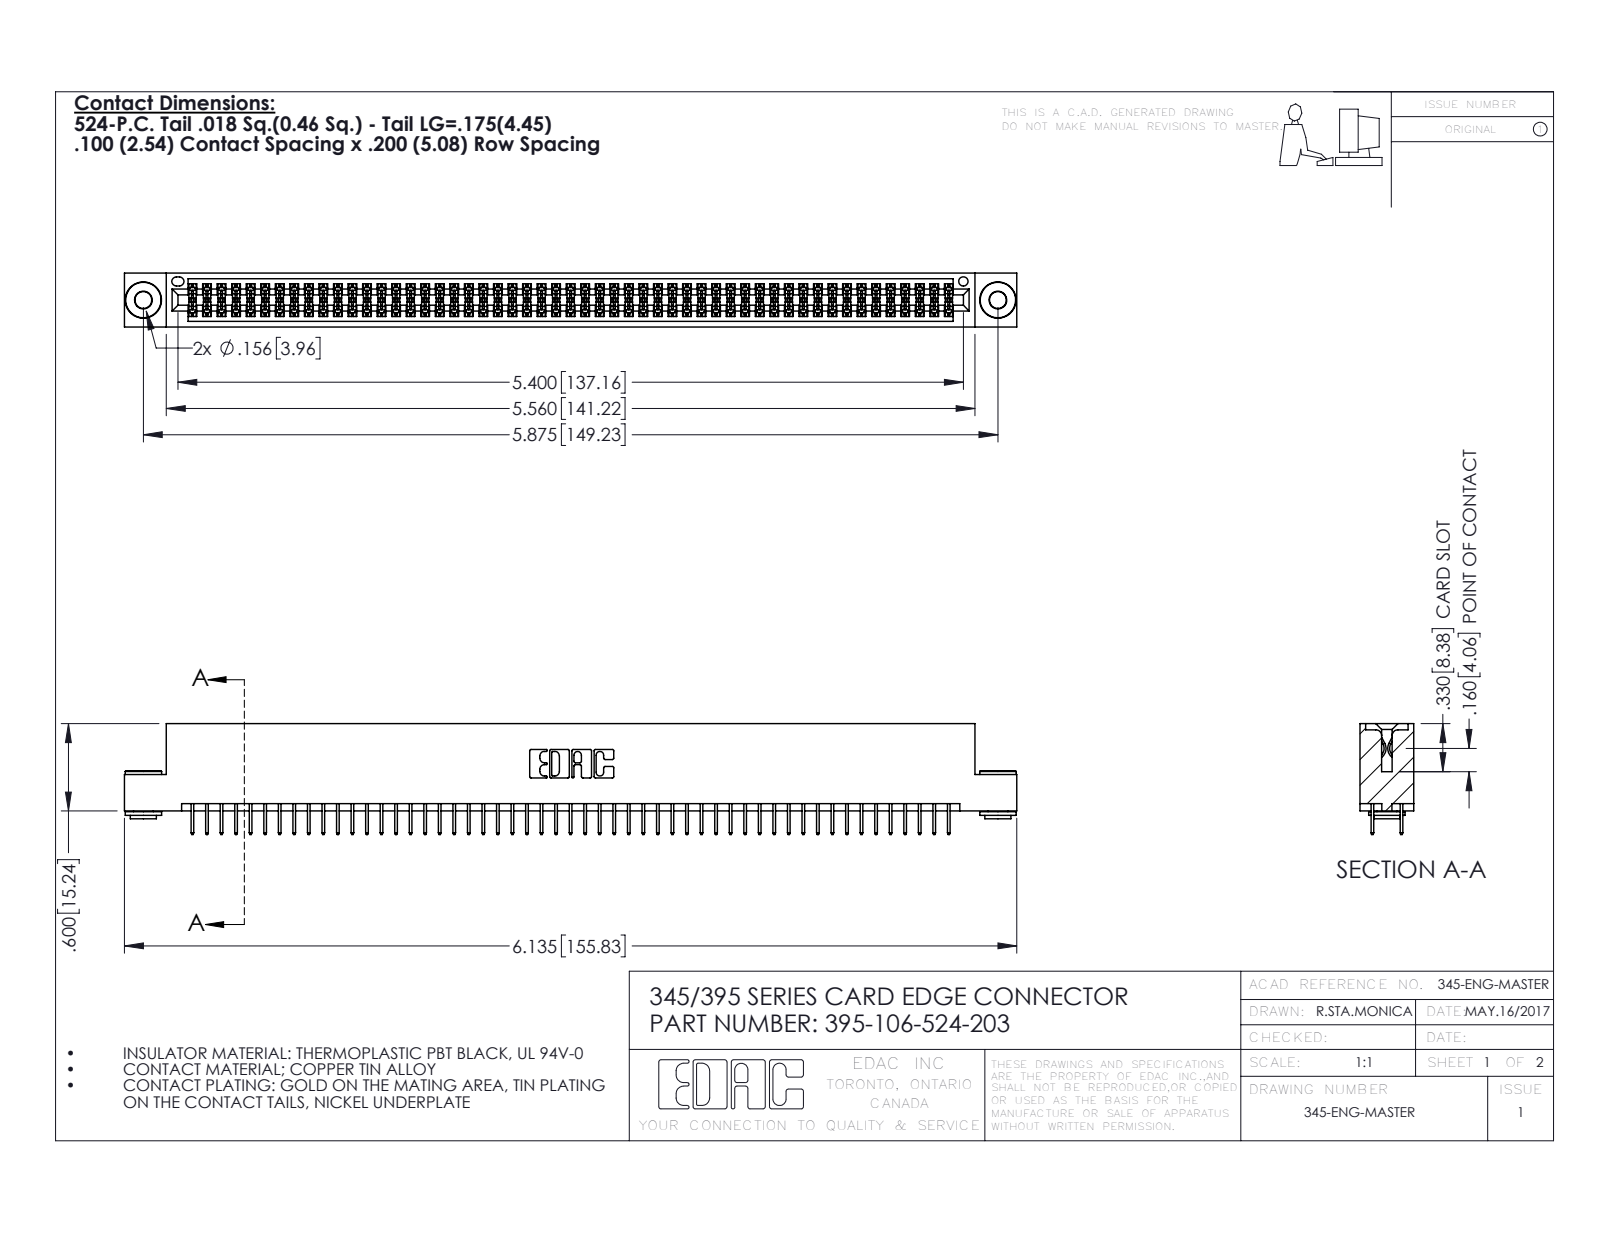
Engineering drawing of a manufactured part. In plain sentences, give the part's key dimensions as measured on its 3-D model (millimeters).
The part is named "345-250-002_345-250-002-102; 345 Part_Flush Mounting Lugs - 0.156 Dia-TH; 395-106-524-203; 345-292-001_345-293-124". Its 3-D file was written by "SolidWorks 2016 (CONFIG_CONTROL_DESIGN)". It is 109 solids with 5888 faces: 4224 planar, 1656 cylindrical and 8 other. Overall it measures 155.8 by 19.4 by 9.4 millimeters. Its volume is 15 100 cubic millimeters and its surface area 22 310 square millimeters. Round holes: 2 of diameter 2.9, 2 of diameter 4, 1 of diameter 1.6. Round bosses or shafts: 2 of diameter 6.4, 2 of diameter 4.6, 2 of diameter 3.5. Partial cylindrical surfaces (rounded edges, fillets, slot ends): 159 of radius 0.2, 22 of radius 0.3, 6 of radius 0.2, 6 of radius 0.8, 3 of radius 0.7, 2 of radius 0.4, 2 of radius 0.5, 2 of radius 0.6. The main face-to-face distances are 1.8, 7.6, 5.1, 9.4, 0.6, 2.5, 6.9, 5.7, 1.8, 4.4. The hole center spacings are 6.9, 143.2, 149.2.
